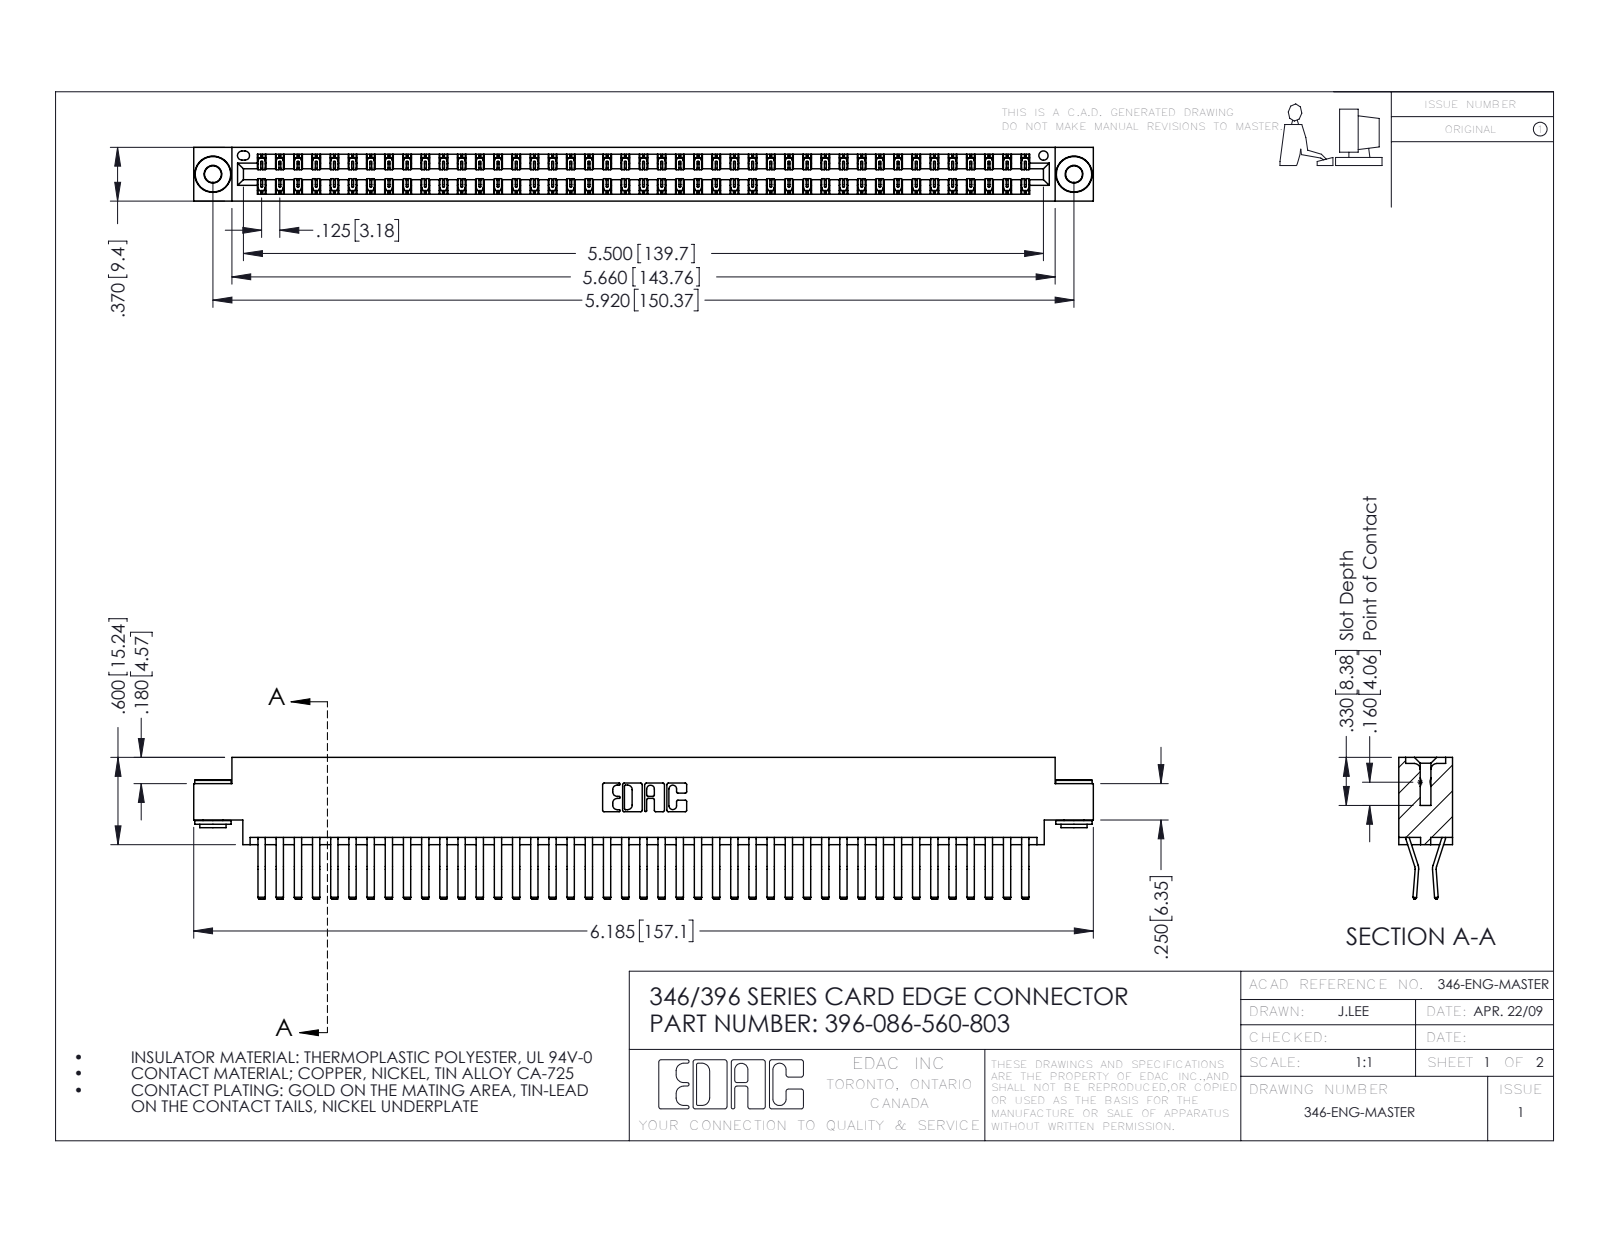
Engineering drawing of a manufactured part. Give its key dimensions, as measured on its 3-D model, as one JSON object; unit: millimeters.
{"part_name": "345-250-002_345-250-002-102; 396-086-560-803; 345-292-001_560 Tail; 346 Part_0.170 Offset - 0.156 Dia-TH", "step_written_by": "SolidWorks 2016 (CONFIG_CONTROL_DESIGN)", "units": "millimeters", "bodies": {"solids": 89, "faces": 4808, "planar": 3100, "cylindrical": 1700, "other": 8}, "overall_size": [157.1, 24.8, 9.4], "volume_mm3": 15700, "surface_area_mm2": 23570, "round_holes": [[2.9, 2], [4, 2], [1.6, 1]], "round_bosses_or_shafts": [[6.4, 2], [4.6, 2], [3.5, 2]], "partial_cylinders_radius": [[0.2, 129], [0.3, 22], [0.2, 6], [0.8, 6], [0.7, 3], [0.3, 2], [0.4, 2], [0.6, 2]], "face_to_face_distances": [1.2, 8.2, 9.4, 0.6, 6.4, 7, 1.8, 7.6, 3.8, 5.6], "hole_center_spacings": [6.2, 145.1, 150.4]}
